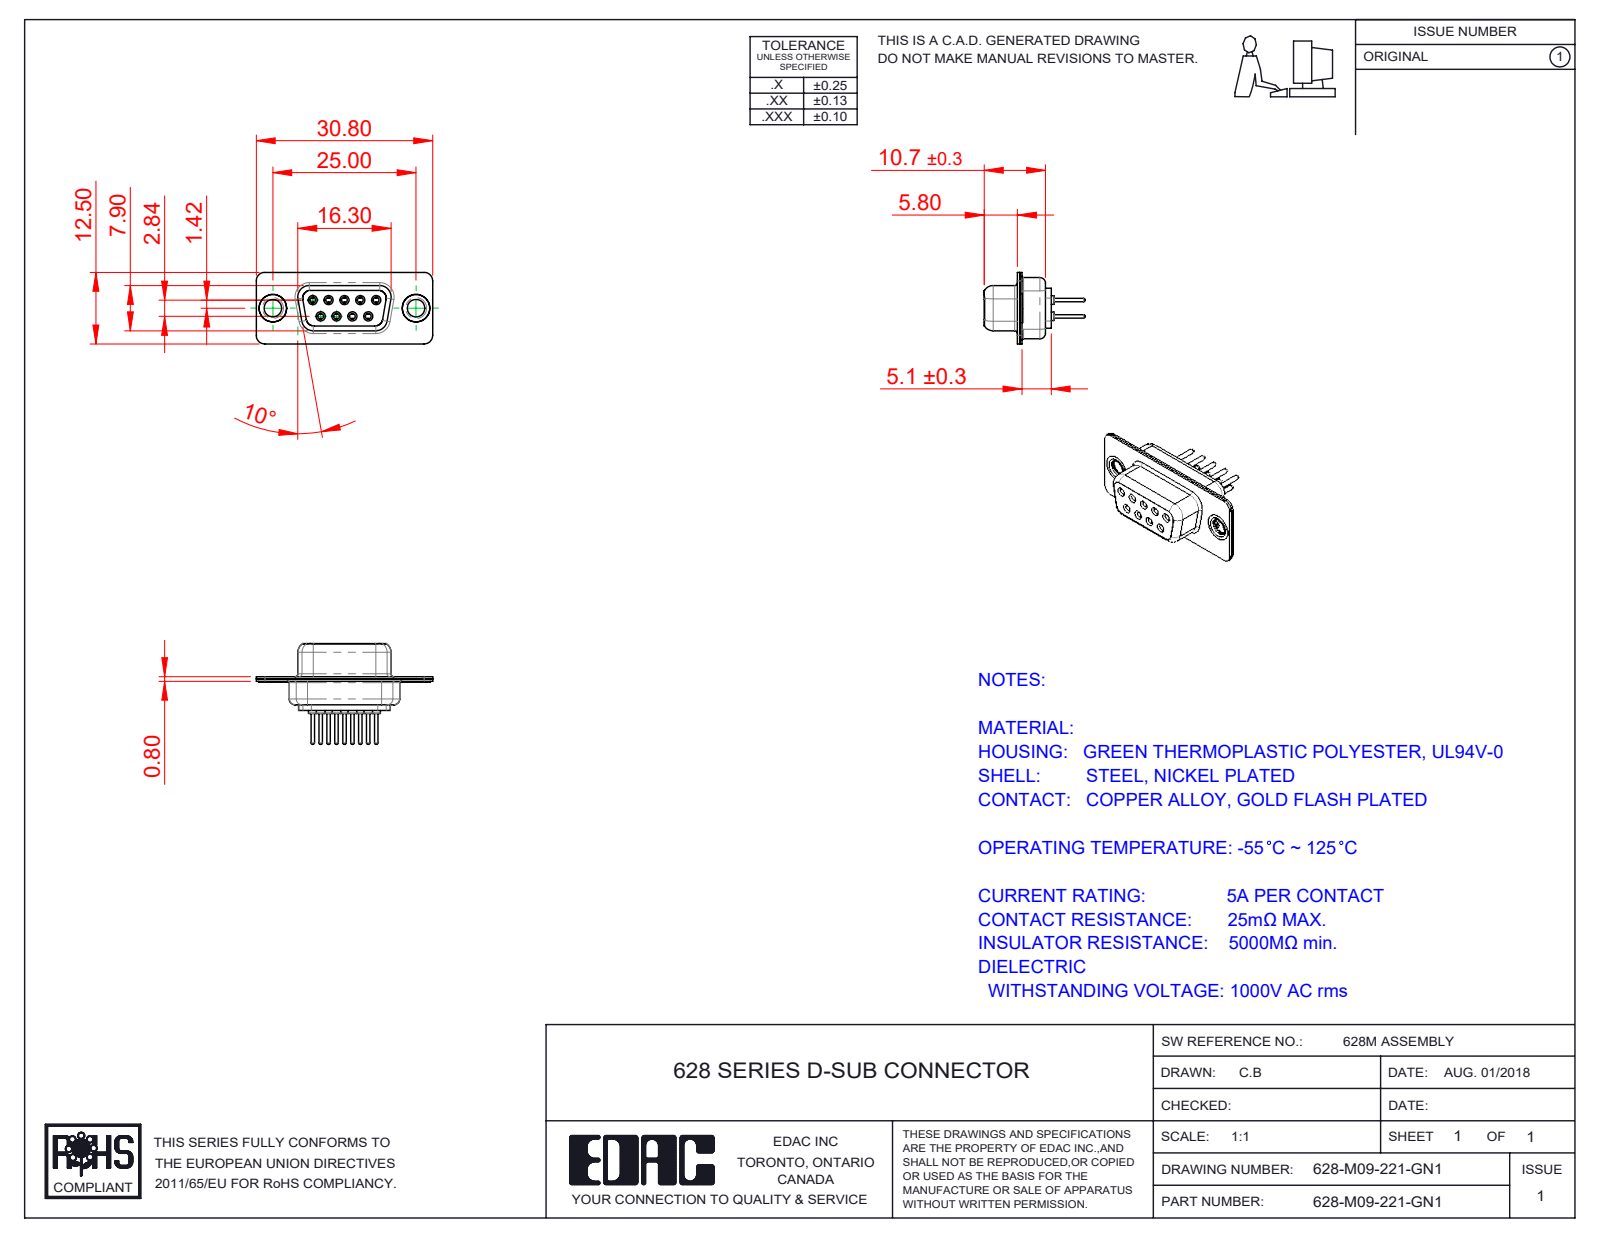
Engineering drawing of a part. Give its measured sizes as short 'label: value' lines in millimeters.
name: 628M Contact Row 1_21; 628M Housing_09 Contacts; 628-M09-221-GN1; 628M Thru Hole Rivet (+3 more)
written by: SolidWorks 2020 (CONFIG_CONTROL_DESIGN)
unit: mm
bodies: 14 solids, 748 faces (202 planar, 292 cylindrical, 254 other)
size: 30.8 × 17.6 × 12.5
volume: 1 624 mm³; area: 4 277 mm²
holes: 9× ⌀1, 9× ⌀1.1, 9× ⌀1.7, 9× ⌀1.8, 9× ⌀2, 2× ⌀3.05, 2× ⌀4, 2× ⌀4.8
bosses: 9× ⌀2.2, 9× ⌀1.6, 9× ⌀1.5, 9× ⌀0.6, 2× ⌀5, 2× ⌀4.9, 2× ⌀3.55
rounds: 16× R1.5, 12× R2, 8× R1.35, 8× R1.6, 4× R0.25, 4× R0.5, 4× R0.6, 4× R0.65
face distances: 0.4, 1.4, 0.45, 8.45, 0.8, 8.9, 1.8, 1, 6.2, 1.35
hole spacings: 3.16, 2.77, 5.54, 5.03, 5.04, 8.31, 7.1, 7.48
